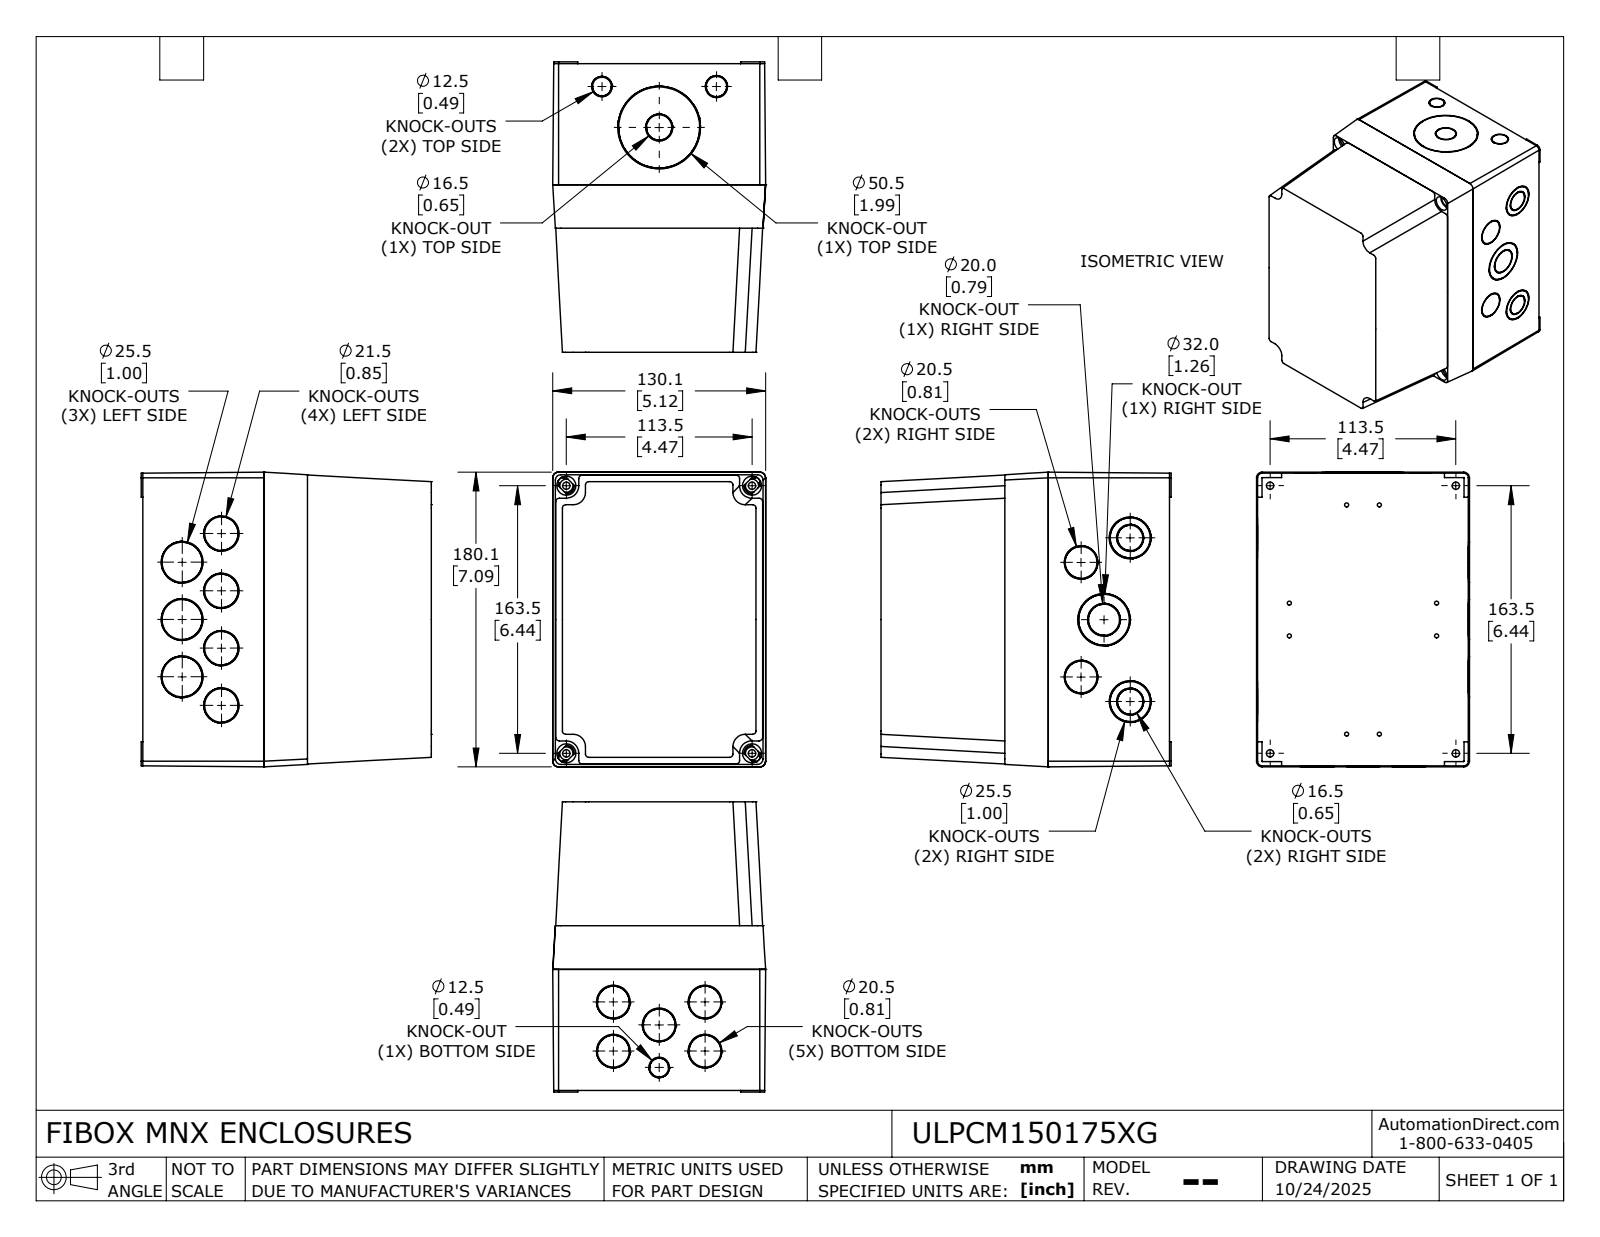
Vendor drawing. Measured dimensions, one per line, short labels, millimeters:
name: ULPCM150175XG
written by: SolidWorks 2024 (AUTOMOTIVE_DESIGN)
unit: mm
bodies: 2 solids, 426 faces (212 planar, 184 cylindrical, 30 other)
size: 180.09 × 177.32 × 130.09
volume: 709 357 mm³; area: 304 397 mm²
holes: 8× ⌀2.5, 8× ⌀3.2, 7× ⌀20.5, 5× ⌀25.5, 4× ⌀4.5, 4× ⌀8, 4× ⌀11.59, 4× ⌀21.5, 1× ⌀12.5, 1× ⌀13.5, 1× ⌀16.5, 1× ⌀20
bosses: 8× ⌀8, 7× ⌀19.5, 5× ⌀24.5, 4× ⌀20.5, 3× ⌀15.5, 2× ⌀11.5, 1× ⌀49.5, 1× ⌀31
rounds: 12× R2, 8× R2.2, 6× R1.21, 4× R0.2, 4× R2.85, 4× R3.29, 4× R3.49, 4× R4.86
face distances: 4.22, 4.2, 172.12, 176.32, 3, 169.12, 173.32, 114.16, 164.15, 14.11
hole spacings: 10, 29.7, 35, 90, 20, 33.85, 40, 40.31
